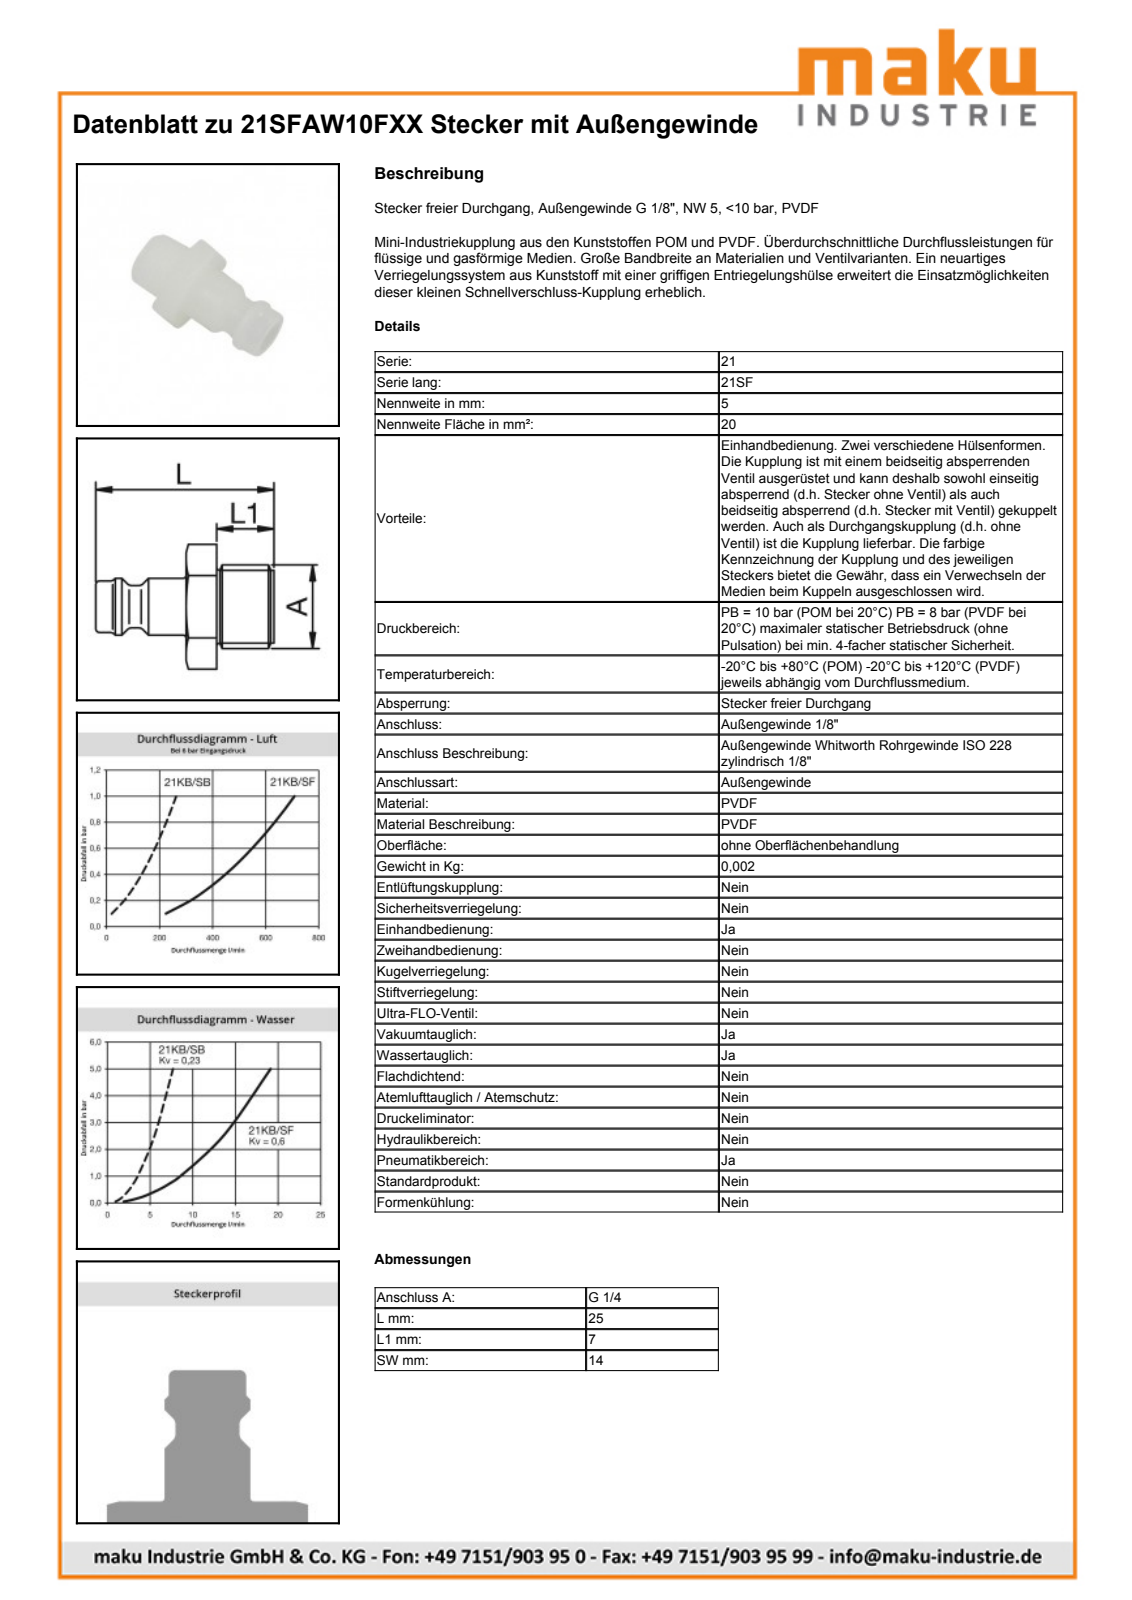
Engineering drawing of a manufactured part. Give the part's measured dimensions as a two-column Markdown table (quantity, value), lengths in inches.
| quantity | value |
| --- | --- |
| part name | D108932 |
| STEP written by | Autodesk Inventor 2013 (AUTOMOTIVE_DESIGN) |
| units | inches |
| bodies | 1 solid, 296 faces (109 planar, 33 cylindrical, 154 other) |
| overall size | 0.984 × 0.754 × 0.669 |
| volume | 0.103 in³ |
| surface area | 2.542 in² |
| round holes (diameter × count) | 0.195 × 1 |
| round bosses / shafts (diameter × count) | 0.383 × 1, 0.354 × 1, 0.335 × 1, 0.319 × 1, 0.262 × 1 |
| partial cylindrical surfaces (radius × count) | 0.163 × 1, 0.377 × 1 |
| main face-to-face distances | 0.154, 0.669, 0.555, 0.709, 0.984, 0.429, 0.276, 0.474, 0.081, 0.234 |
